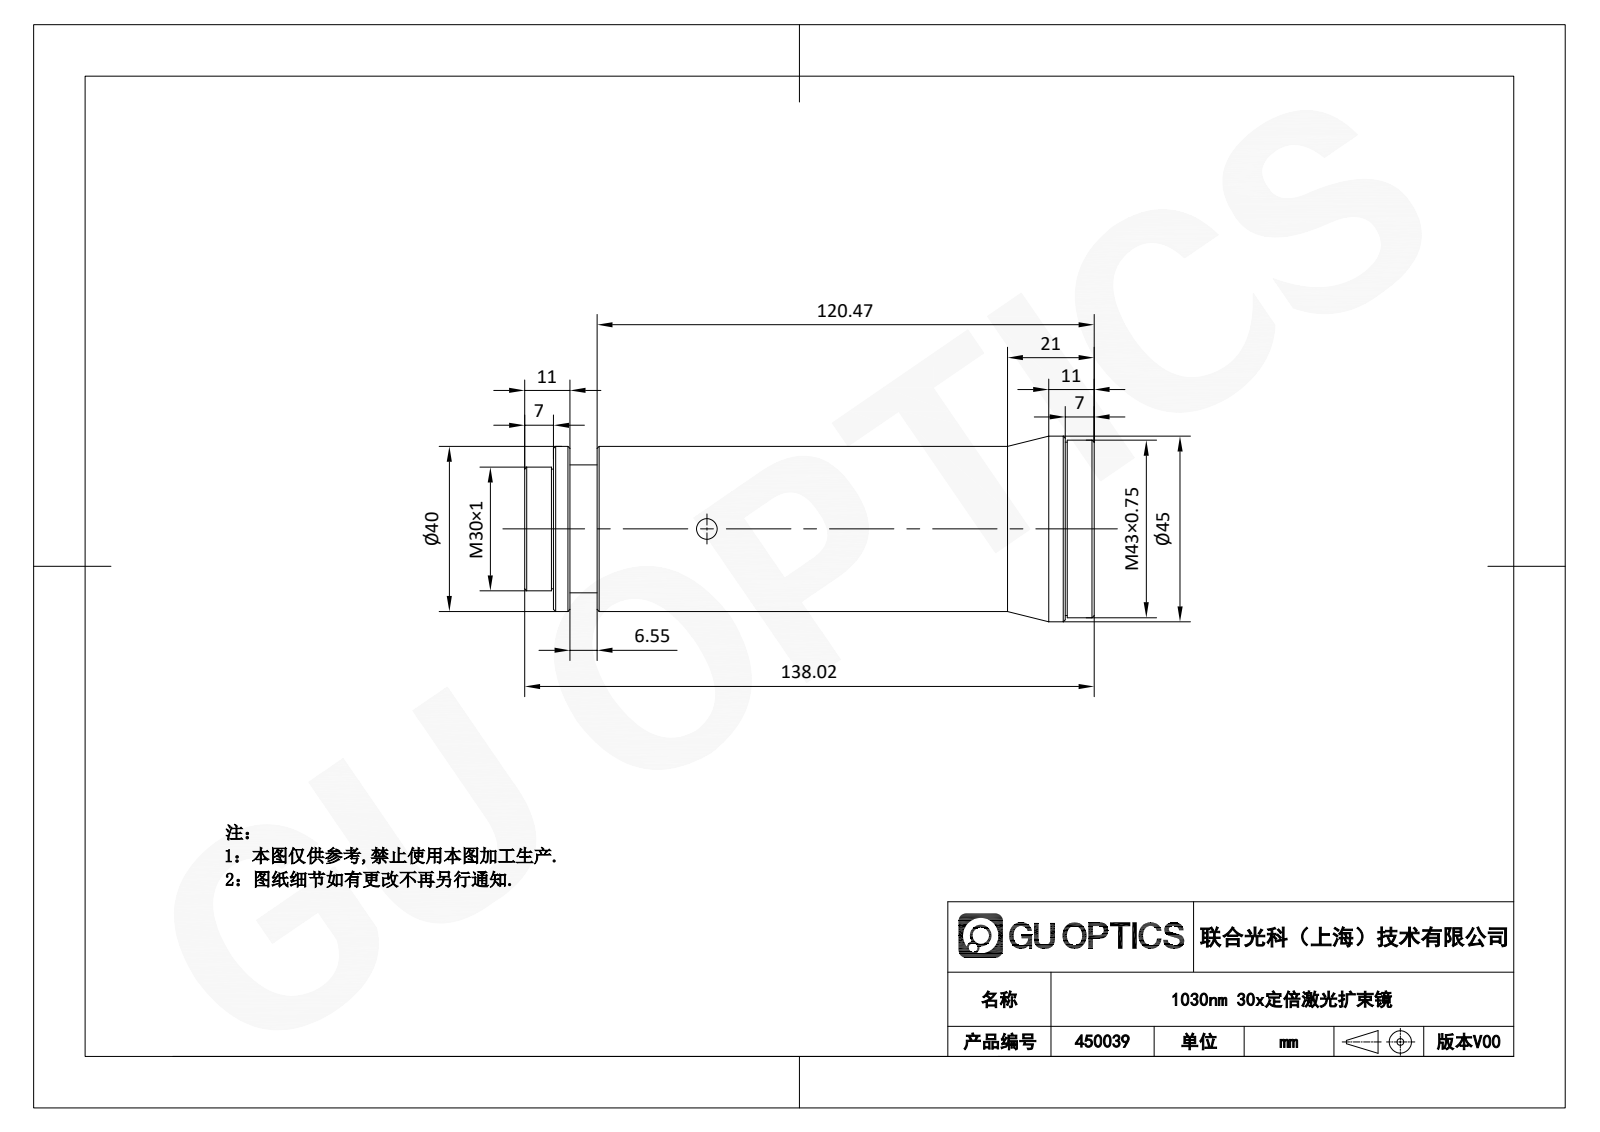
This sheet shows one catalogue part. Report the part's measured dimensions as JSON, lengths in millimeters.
{"part_name": "450039", "step_written_by": "SolidWorks 2020 (CONFIG_CONTROL_DESIGN)", "units": "millimeters", "bodies": {"solids": 1, "faces": 29, "planar": 9, "cylindrical": 18, "other": 2}, "overall_size": [138.02, 45, 45], "volume_mm3": 170197, "surface_area_mm2": 21574, "round_holes": [[5, 1]], "round_bosses_or_shafts": [[45, 1], [43, 1], [42, 1], [40, 1], [31, 1], [30, 1], [29, 1]], "face_to_face_distances": [7, 131.02, 138.02, 11, 17.55, 4, 10.55, 6.55, 127.02, 120.47]}
